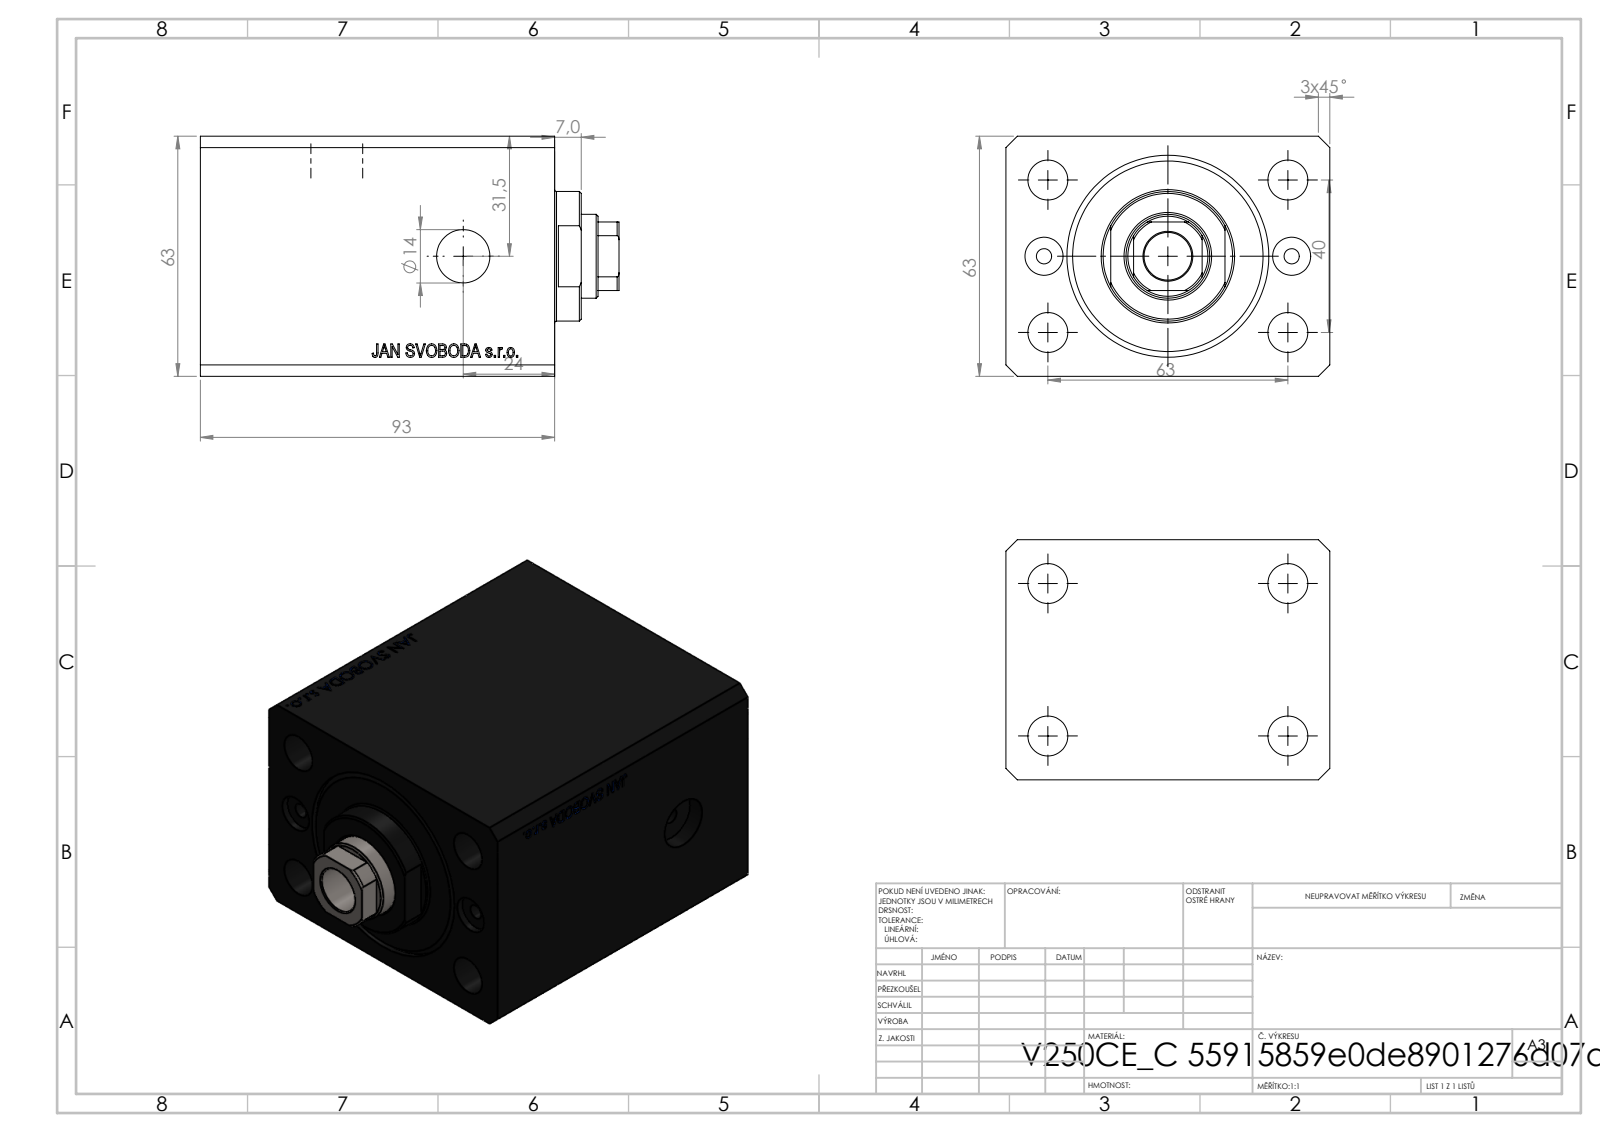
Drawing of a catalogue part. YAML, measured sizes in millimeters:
part_name: "V250CE_VC_C; V250CE_C_Body; V250CE_C_VCP"
step_written_by: "SolidWorks 2019 (CONFIG_CONTROL_DESIGN)"
units: millimeters
bodies: {solids: 3, faces: 864, planar: 428, cylindrical: 44, other: 392}
overall_size: [110, 85, 63]
volume: 450054
surface_area: 83653
round_holes:
  - {diameter: 4, count: 4}
  - {diameter: 10.5, count: 4}
  - {diameter: 10, count: 2}
  - {diameter: 14, count: 2}
  - {diameter: 12.5, count: 1}
  - {diameter: 22, count: 1}
  - {diameter: 40, count: 1}
  - {diameter: 53, count: 1}
round_bosses_or_shafts:
  - {diameter: 34, count: 1}
partial_cylinders:
  - {radius: 10.5, count: 1}
face_to_face_distances: [63, 85, 93, 17, 76, 11.4, 64.6, 81.6, 56, 44.6]
hole_center_spacings: [20.02, 37.31, 67.05, 32.5, 40, 63, 74.63, 45]
